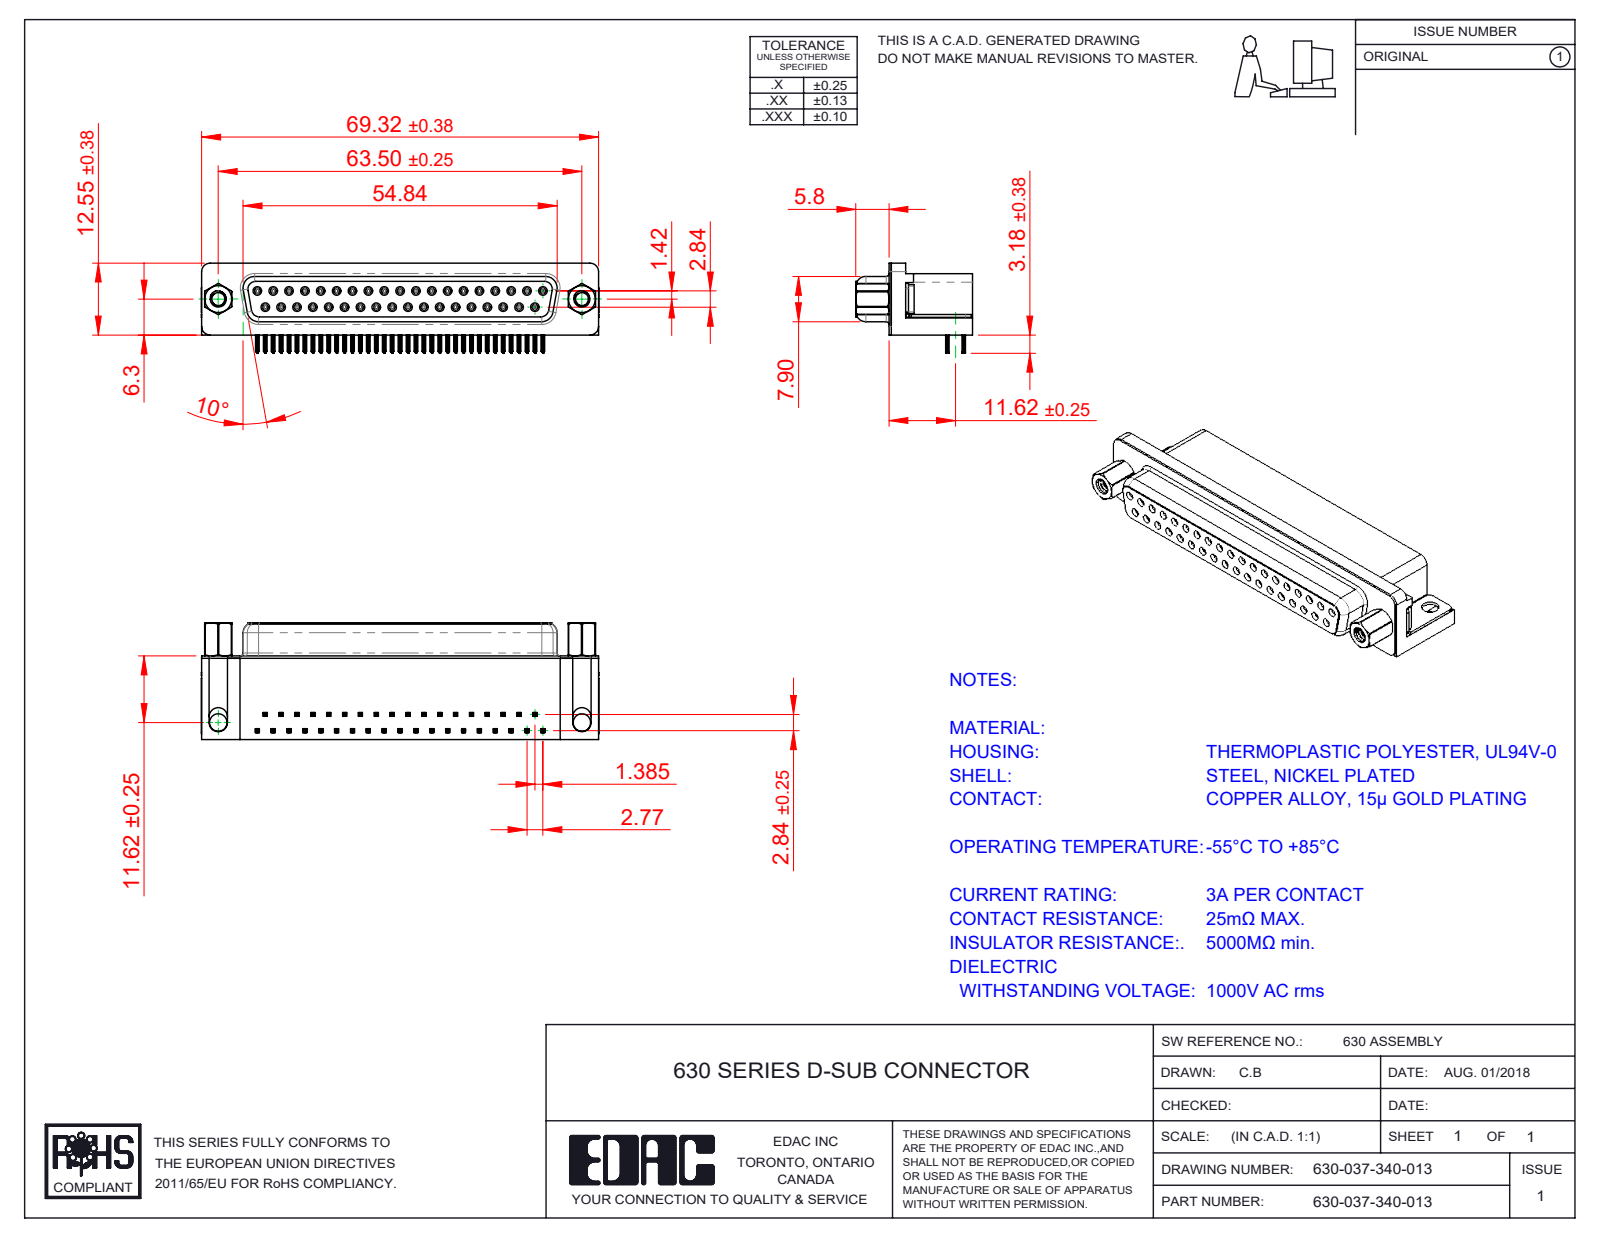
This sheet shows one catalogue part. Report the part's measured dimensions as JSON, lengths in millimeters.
{"part_name": "630-037-340-013; 630 Housing_37 Socket; 630 Shell_37 Socket; 630 Contact Bottom (+4 more)", "step_written_by": "SolidWorks 2020 (CONFIG_CONTROL_DESIGN)", "units": "millimeters", "bodies": {"solids": 45, "faces": 5686, "planar": 2524, "cylindrical": 1370, "other": 1792}, "overall_size": [69.4, 20.4, 15.73], "volume_mm3": 12027, "surface_area_mm2": 14018, "round_holes": [[0.8, 37], [0.9, 37], [2.26, 2], [2.29, 2], [3.05, 2], [4, 2], [4.8, 2], [5, 2]], "round_bosses_or_shafts": [[1.2, 37], [4.9, 2], [4.75, 2], [3.9, 2], [2.79, 2]], "partial_cylinders_radius": [[0.1, 296], [0.15, 148], [0.35, 74], [0.34, 37], [0.28, 18], [1, 18], [0.25, 8], [1.35, 8]], "face_to_face_distances": [0.4, 6.2, 10.34, 14.2, 6.65, 0.85, 2.84, 14.6, 0.45, 5.8], "hole_center_spacings": [3.16, 2.77, 5.54, 8.31, 11.08, 13.85, 16.62, 19.39]}
